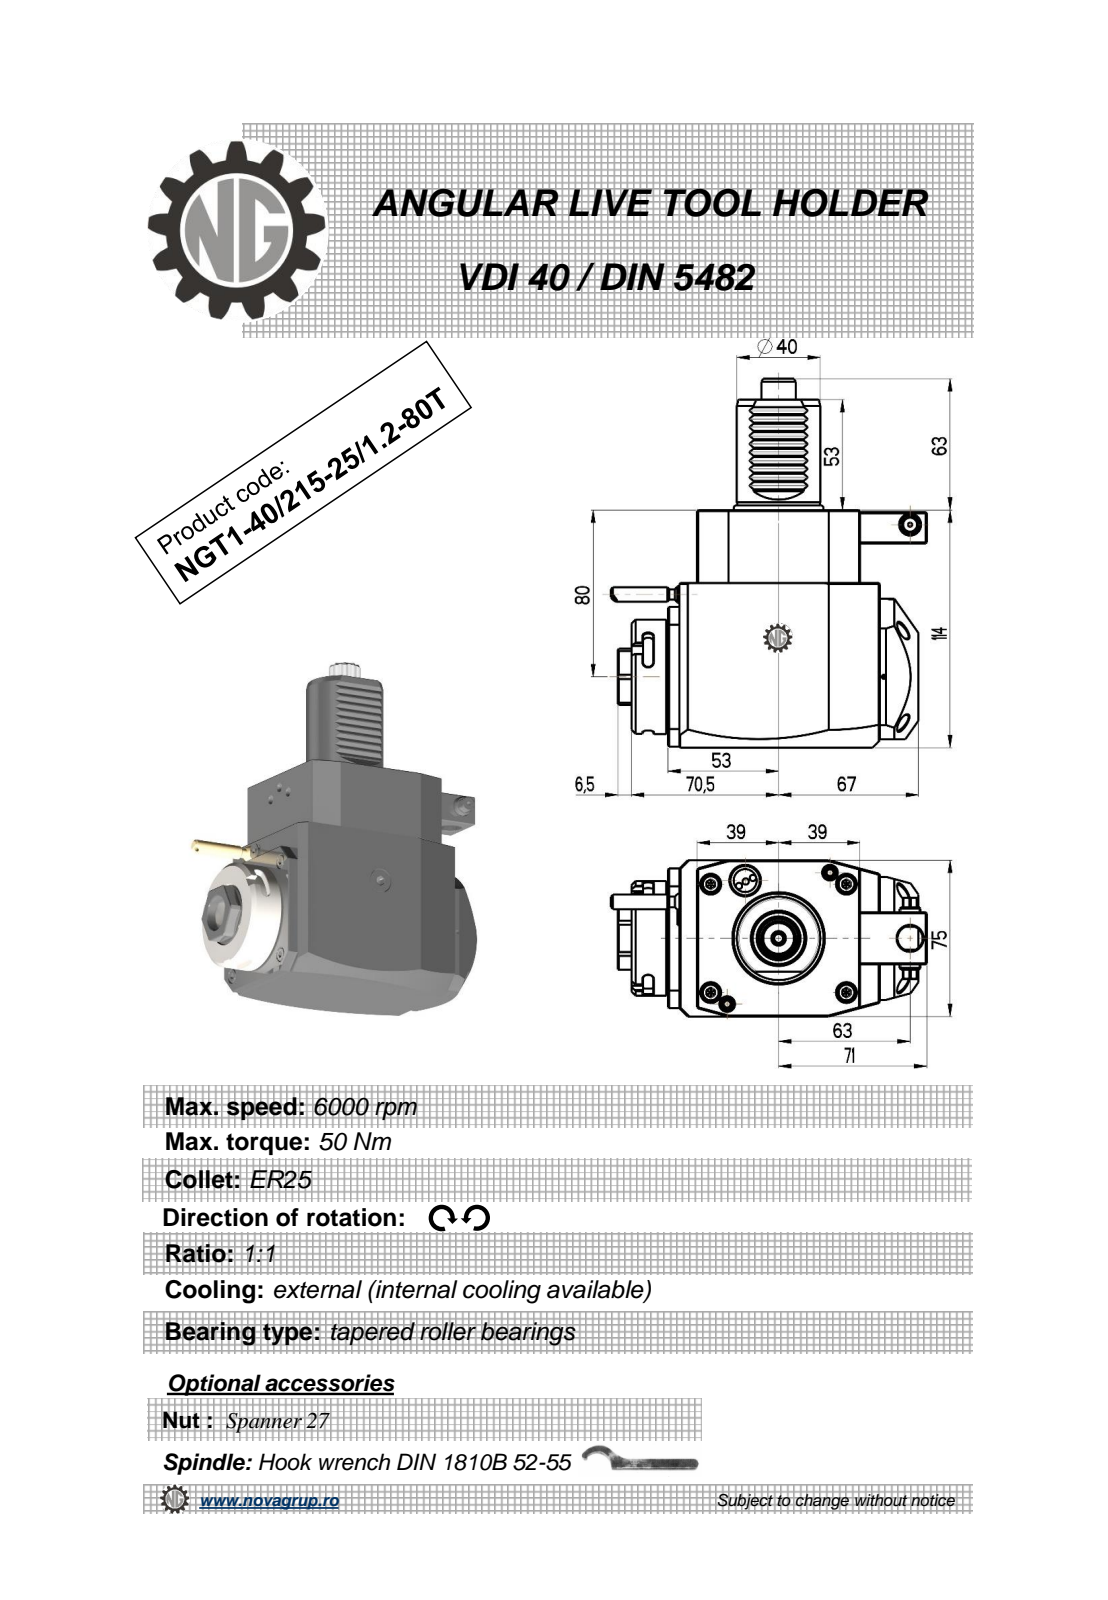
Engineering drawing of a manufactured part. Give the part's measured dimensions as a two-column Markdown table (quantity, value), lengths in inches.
| quantity | value |
| --- | --- |
| part name | NGT1_40_215_25_1_2_80T |
| STEP written by | PRO/ENGINEER BY PARAMETRIC TECHNOLOGY CORPORATION, 2010280 (CONFIG_CONTROL_DESIGN) |
| units | inches |
| bodies | 1 solid, 390 faces (176 planar, 123 cylindrical, 91 other) |
| overall size | 6.969 × 5.958 × 2.953 |
| volume | 57.79 in³ |
| surface area | 108.9 in² |
| round holes (diameter × count) | 0.079 × 1, 0.098 × 1, 0.118 × 1, 0.165 × 1, 0.209 × 1, 0.374 × 1, 0.472 × 1, 0.709 × 1 |
| round bosses / shafts (diameter × count) | 0.315 × 2, 2.165 × 1, 1.89 × 1, 1.575 × 1, 0.394 × 1, 0.276 × 1, 0.197 × 1 |
| partial cylindrical surfaces (radius × count) | 0.119 × 18, 0.012 × 10, 0.098 × 6, 7.087 × 2, 0.02 × 1, 0.152 × 1, 0.167 × 1, 0.266 × 1 |
| main face-to-face distances | 2.953, 4.488, 0.551, 0.689, 3.622, 3.071, 4.311, 1.24, 0.157, 1.102 |
| hole center spacings | 1.47, 1.701, 2.48, 2.854 |
